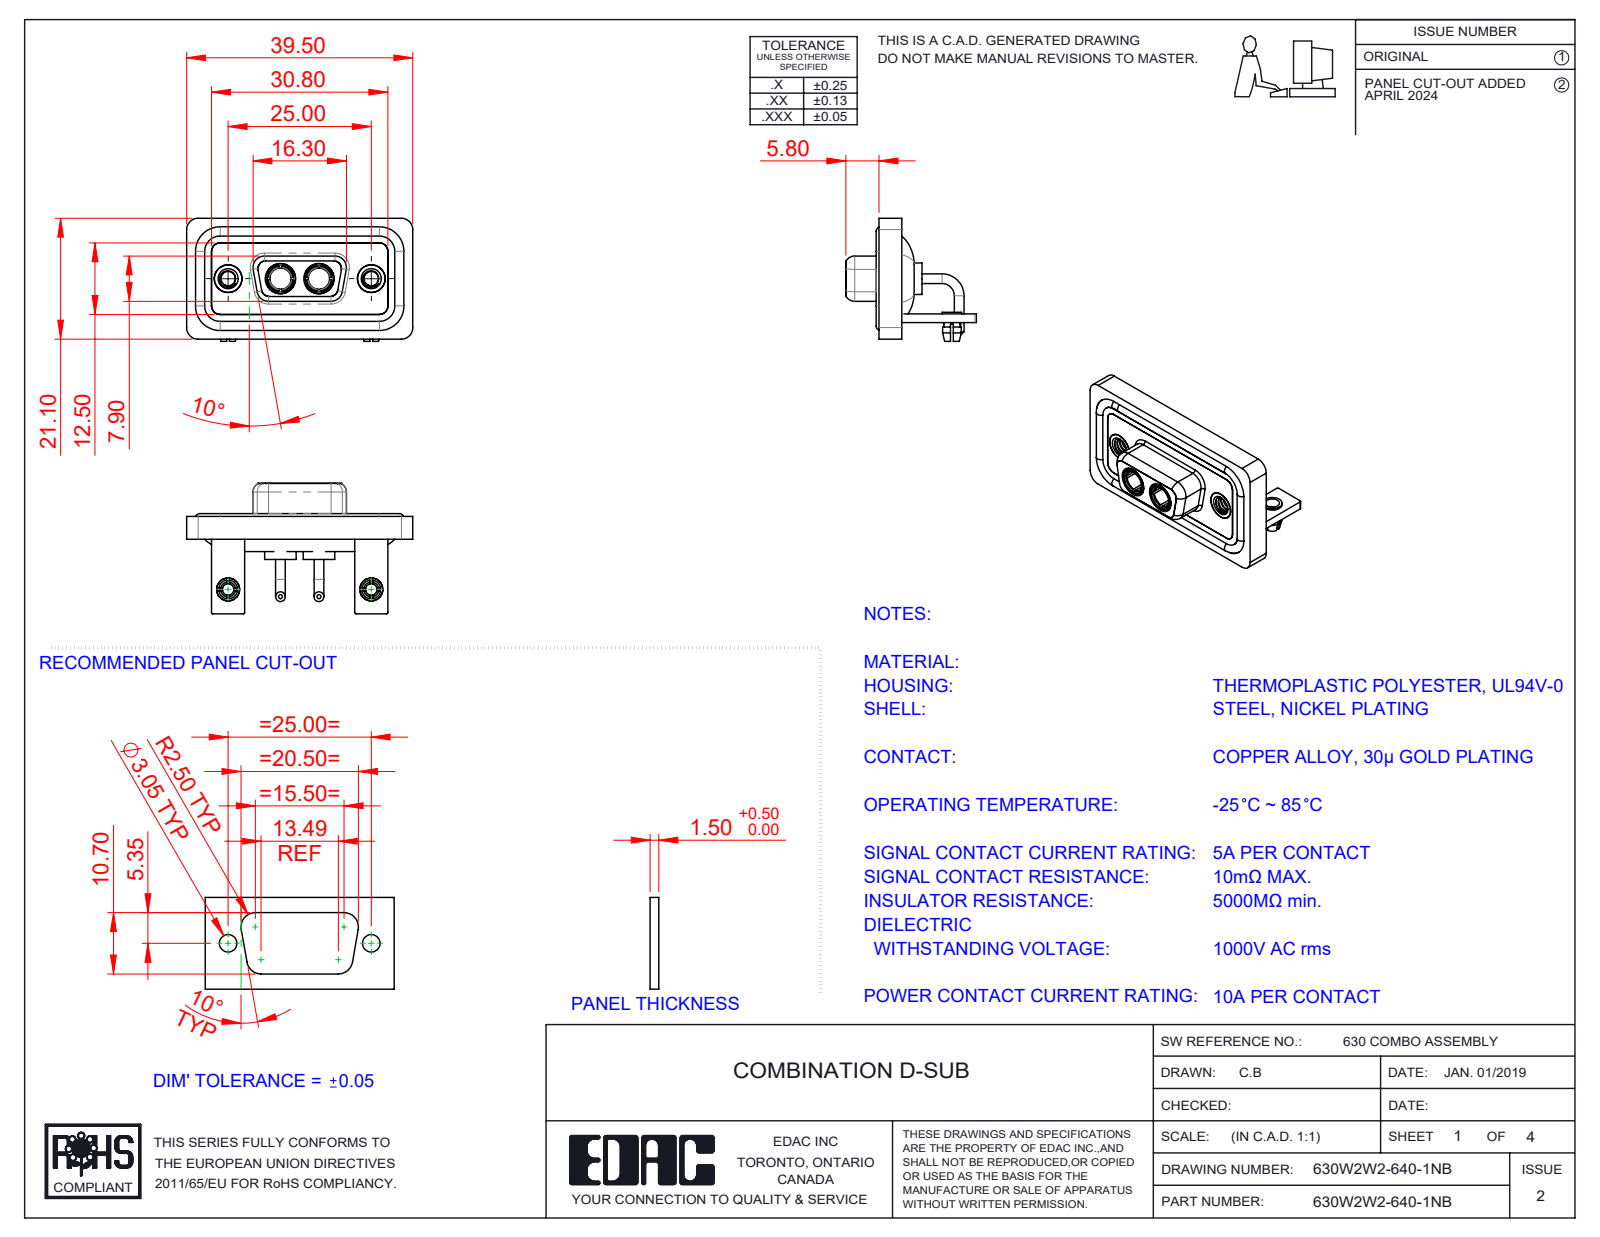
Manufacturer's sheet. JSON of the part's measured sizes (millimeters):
{"part_name": "630Combo Board Lock_50 Contacts; 630Combo Shell Rear_09 Contacts; 630Combo Housing_2W2; 630Combo Threaded Rivet_A (+5 more)", "step_written_by": "SolidWorks 2023 (CONFIG_CONTROL_DESIGN)", "units": "millimeters", "bodies": {"solids": 15, "faces": 676, "planar": 231, "cylindrical": 292, "other": 153}, "overall_size": [39.5, 22.8, 21.5], "volume_mm3": 5096, "surface_area_mm2": 8633, "round_holes": [[2.5, 4], [4.85, 4], [2, 2], [3.2, 2], [3.7, 2], [4, 2], [4.05, 2], [5, 2], [5.3, 2]], "round_bosses_or_shafts": [[1.7, 4], [1.6, 4], [5.5, 2], [5.2, 2], [4.96, 2], [4.95, 2], [4.8, 2], [4.75, 2]], "partial_cylinders_radius": [[2, 19], [1.5, 18], [0.25, 16], [1.35, 8], [1.6, 8], [0.5, 5], [0.6, 4], [0.65, 4]], "face_to_face_distances": [0.4, 2.9, 1.5, 1.8, 1.1, 3.7, 0.8, 2.5, 1.6, 3.1], "hole_center_spacings": [9.14, 15.86, 25, 6.72]}
